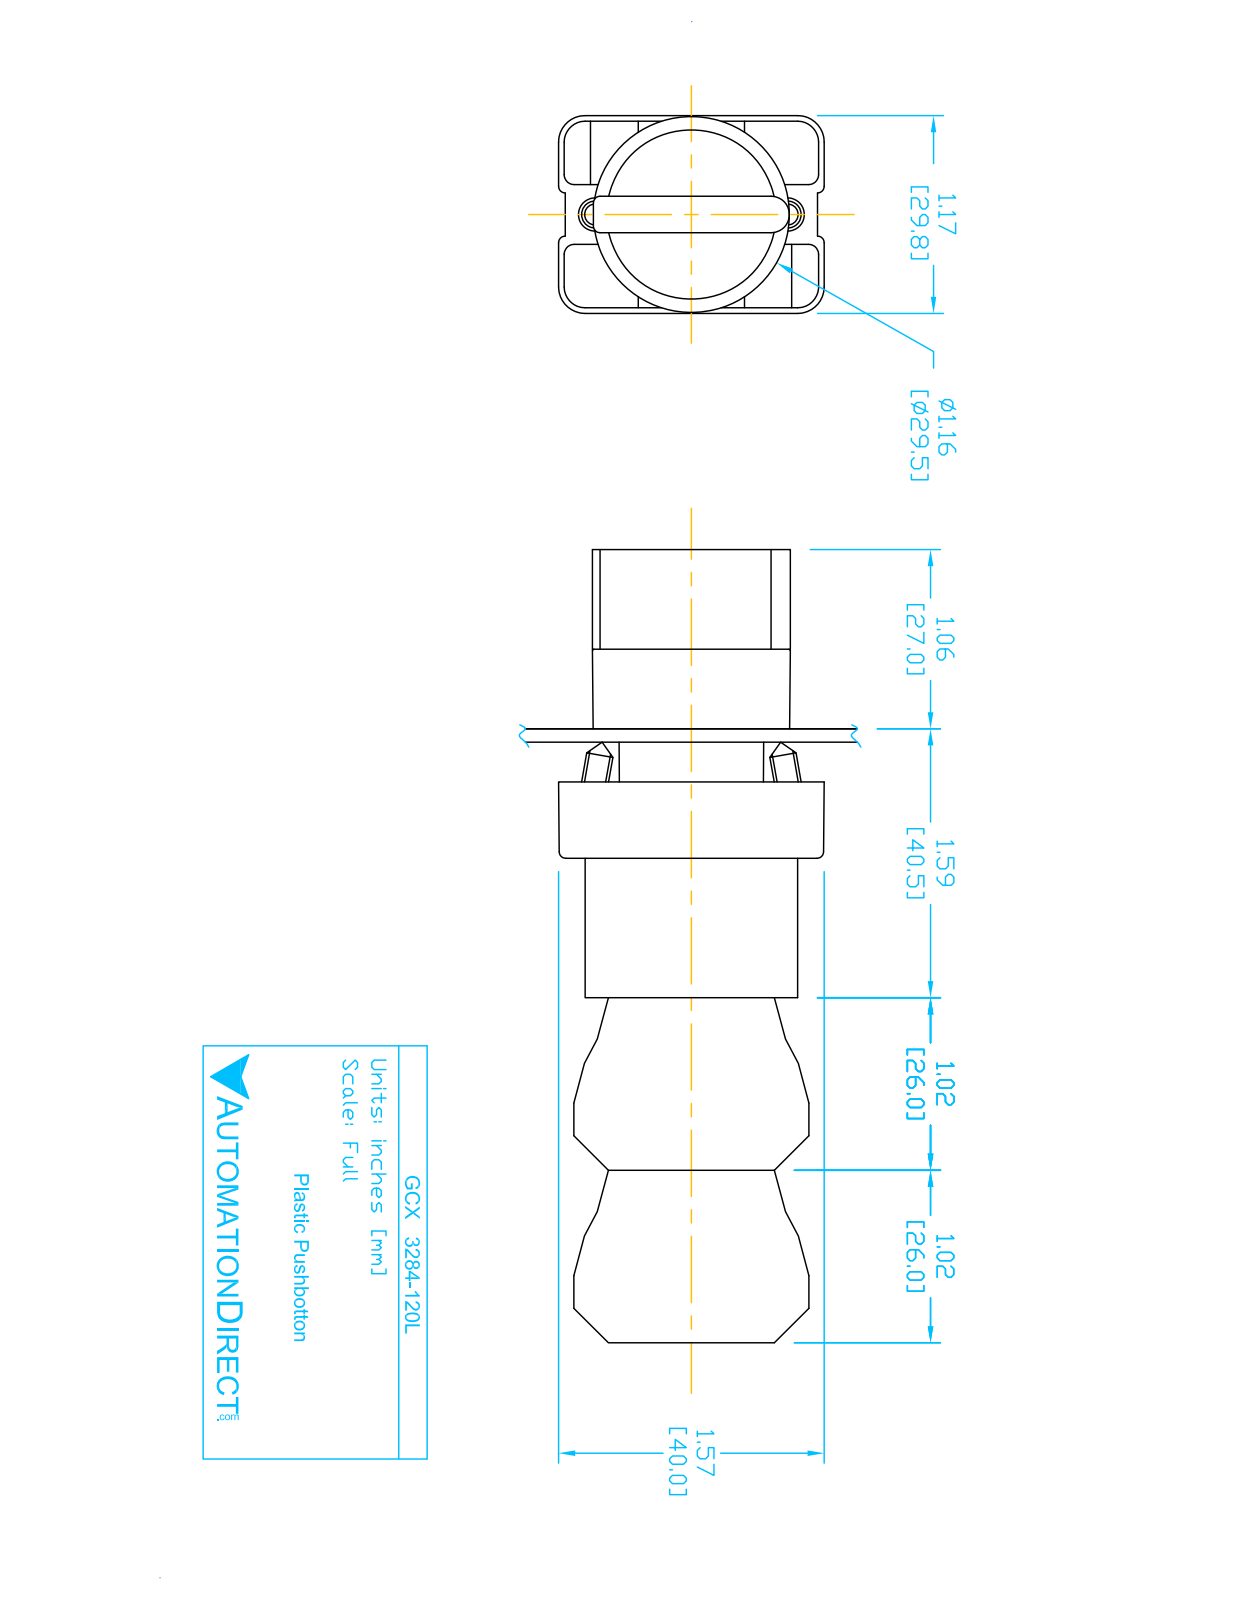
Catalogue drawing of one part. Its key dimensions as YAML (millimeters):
part_name: "ecx1040; ECX3029-2; ECX1050; GCX3284-120L (+2 more)"
step_written_by: "SolidWorks 2016 (AUTOMOTIVE_DESIGN)"
units: millimeters
bodies: {solids: 11, faces: 724, planar: 488, cylindrical: 193, other: 43}
overall_size: [118.8, 40.2, 29.9]
volume: 77850
surface_area: 38210
round_holes:
  - {diameter: 2, count: 4}
  - {diameter: 2.2, count: 2}
  - {diameter: 3.1, count: 2}
  - {diameter: 3.3, count: 2}
  - {diameter: 5, count: 1}
  - {diameter: 11.9, count: 1}
  - {diameter: 22.3, count: 1}
  - {diameter: 22.6, count: 1}
  - {diameter: 26, count: 1}
round_bosses_or_shafts:
  - {diameter: 4, count: 4}
  - {diameter: 29.8, count: 1}
  - {diameter: 25.5, count: 1}
  - {diameter: 24, count: 1}
  - {diameter: 21.7, count: 1}
  - {diameter: 19.8, count: 1}
  - {diameter: 12.8, count: 1}
partial_cylinders:
  - {radius: 1.5, count: 24}
  - {radius: 1, count: 12}
  - {radius: 3.1, count: 12}
  - {radius: 4, count: 12}
  - {radius: 1, count: 9}
  - {radius: 0.5, count: 2}
  - {radius: 1.6, count: 2}
  - {radius: 2, count: 2}
face_to_face_distances: [14.7, 15.1, 26, 29.7, 0.4, 21, 47, 77.3, 51.3, 30.3]
hole_center_spacings: [6, 25.5, 24.7, 12, 13.7, 13.8, 27.5, 12.3]
